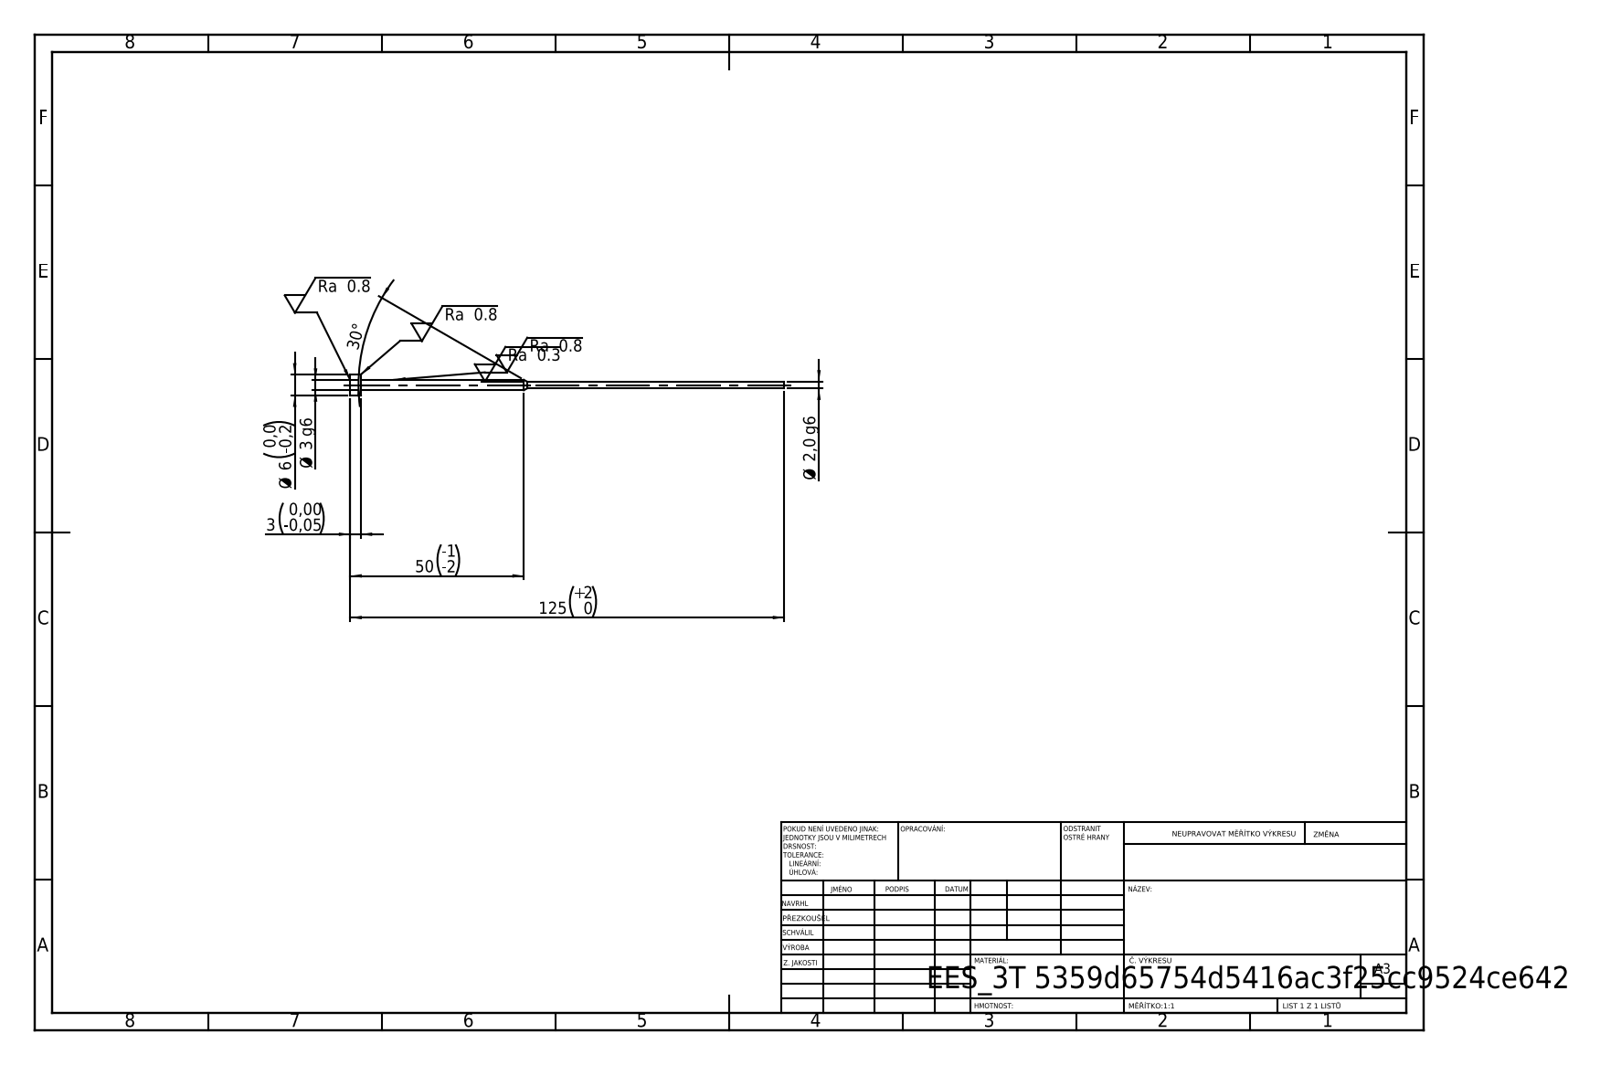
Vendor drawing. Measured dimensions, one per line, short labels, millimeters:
written by: SolidWorks 2019 (CONFIG_CONTROL_DESIGN)
unit: mm
bodies: 1 solid, 11 faces (3 planar, 6 cylindrical, 2 other)
size: 125 × 6 × 6
volume: 654 mm³; area: 1 026 mm²
bosses: 1× ⌀6, 1× ⌀3, 1× ⌀2
face distances: 3, 122, 125
